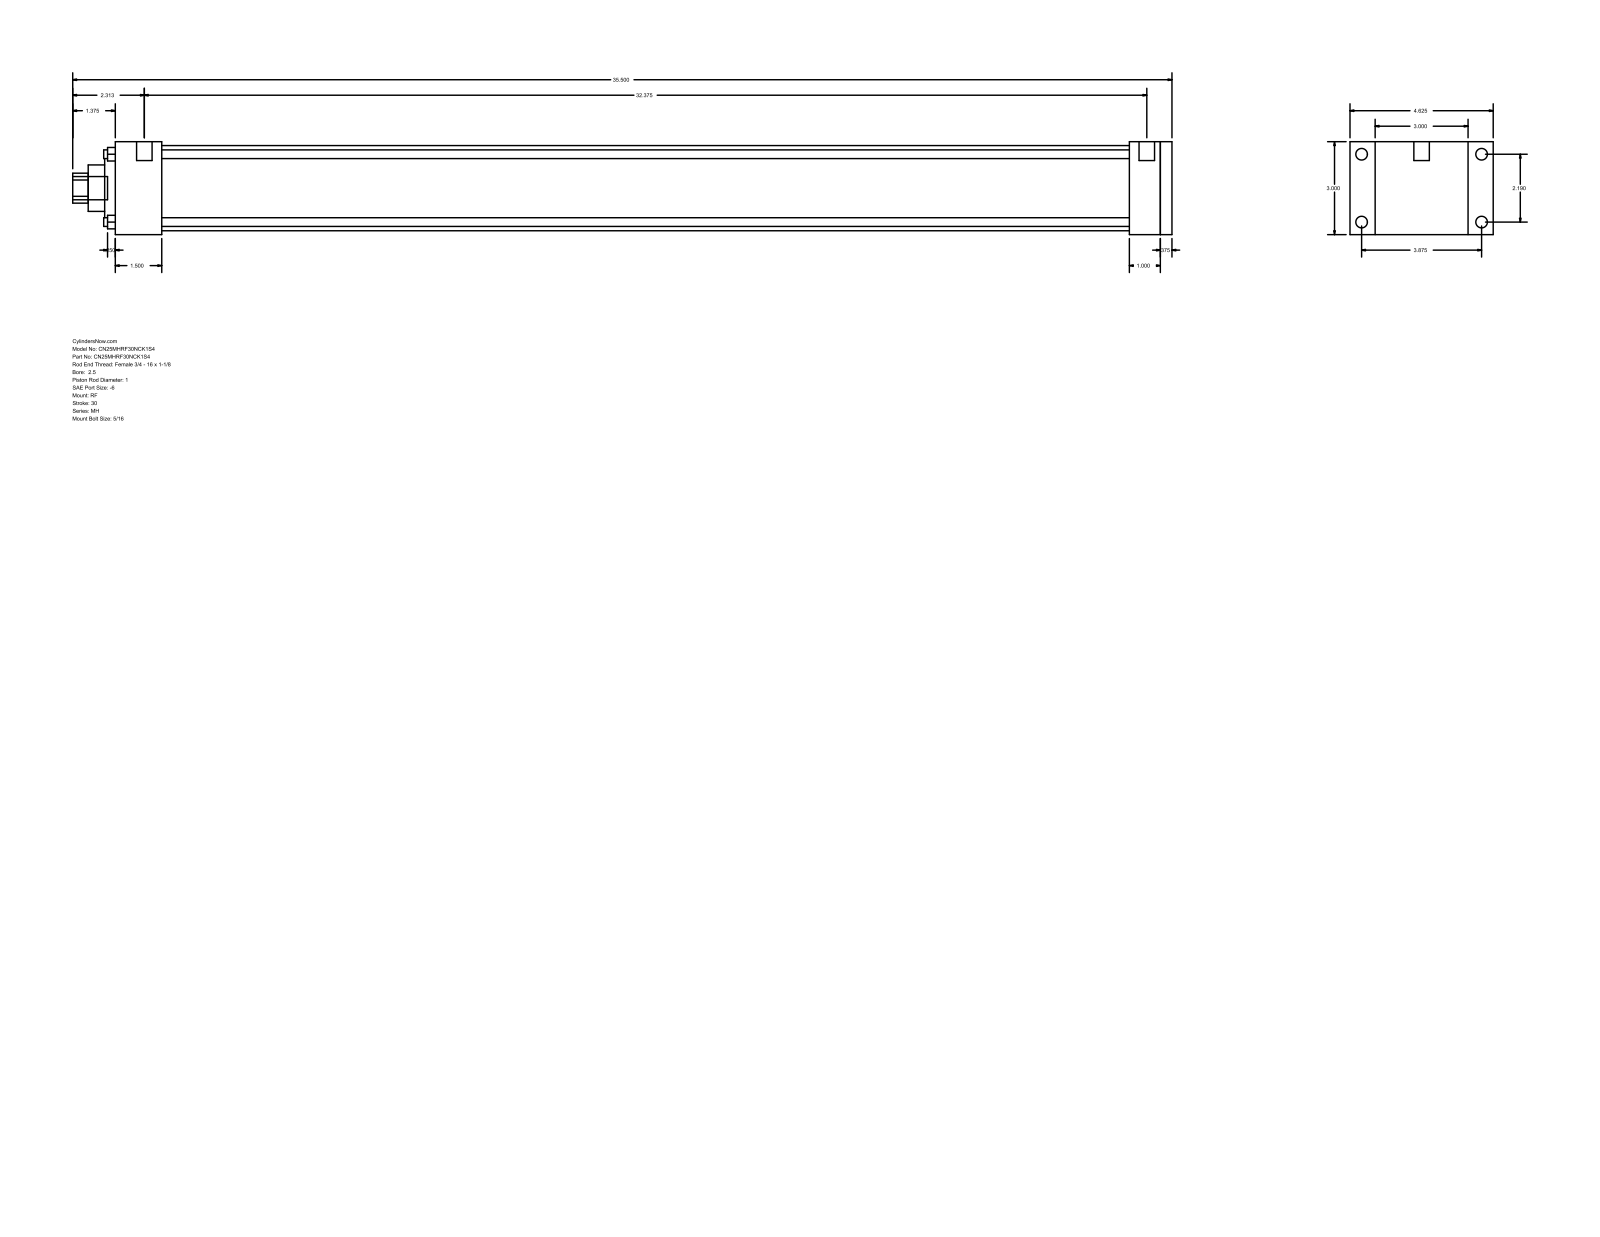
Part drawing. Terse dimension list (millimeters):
name: MH_RF__0250_1
written by: GSSL Pune (CONFIG_CONTROL_DESIGN)
unit: mm
bodies: 0 solids, 94 faces (65 planar, 29 cylindrical, 0 other)
size: 901.7 × 117.47 × 76.2
holes: 4× ⌀7.14, 1× ⌀25.4, 1× ⌀38.1, 1× ⌀60.33, 1× ⌀69.85
bosses: 4× ⌀9.53, 4× ⌀5.56, 2× ⌀12.7, 1× ⌀19.05
rounds: 1× R12.29
face distances: 76.2, 9.53, 857.25, 866.78, 25.4, 831.85, 34.93, 38.11, 793.74, 819.14
hole spacings: 39.33, 55.62, 78.66
